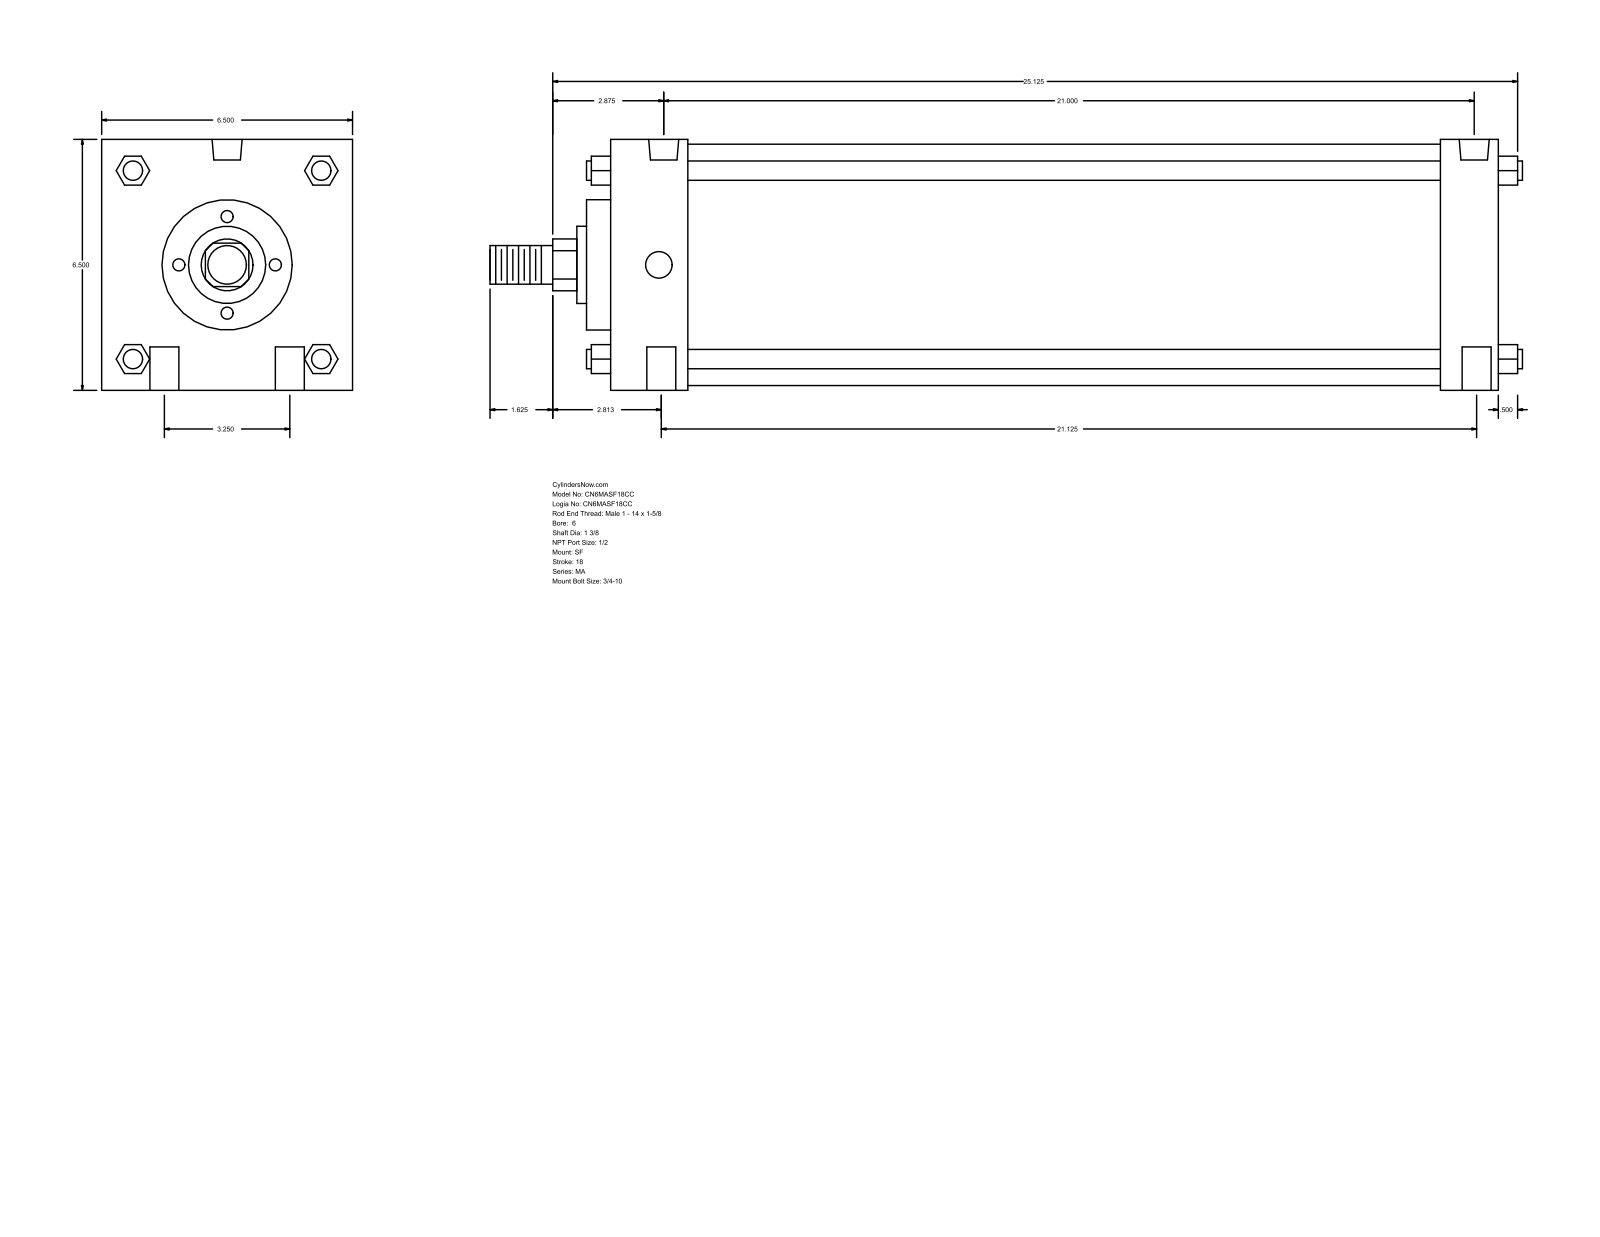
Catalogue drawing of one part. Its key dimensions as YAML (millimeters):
part_name: "MA_SF__0600_1.375"
step_written_by: "GSSL Pune (CONFIG_CONTROL_DESIGN)"
units: millimeters
bodies: {solids: 0, faces: 126, planar: 95, cylindrical: 31, other: 0}
overall_size: [679.45, 165.1, 165.1]
round_holes:
  - {diameter: 19.05, count: 4}
  - {diameter: 17.46, count: 2}
  - {diameter: 19.77, count: 2}
round_bosses_or_shafts:
  - {diameter: 12.7, count: 4}
  - {diameter: 158.75, count: 1}
  - {diameter: 85.72, count: 1}
  - {diameter: 50.8, count: 1}
  - {diameter: 34.92, count: 1}
  - {diameter: 25.4, count: 1}
partial_cylinders:
  - {radius: 17.06, count: 1}
face_to_face_distances: [165.1, 584.2, 546.1, 50.8, 38.1, 495.3, 533.4, 66.67, 15.87, 600.07]
hole_center_spacings: [536.57, 41.3, 82.54, 542.88, 533.39, 533.4]
